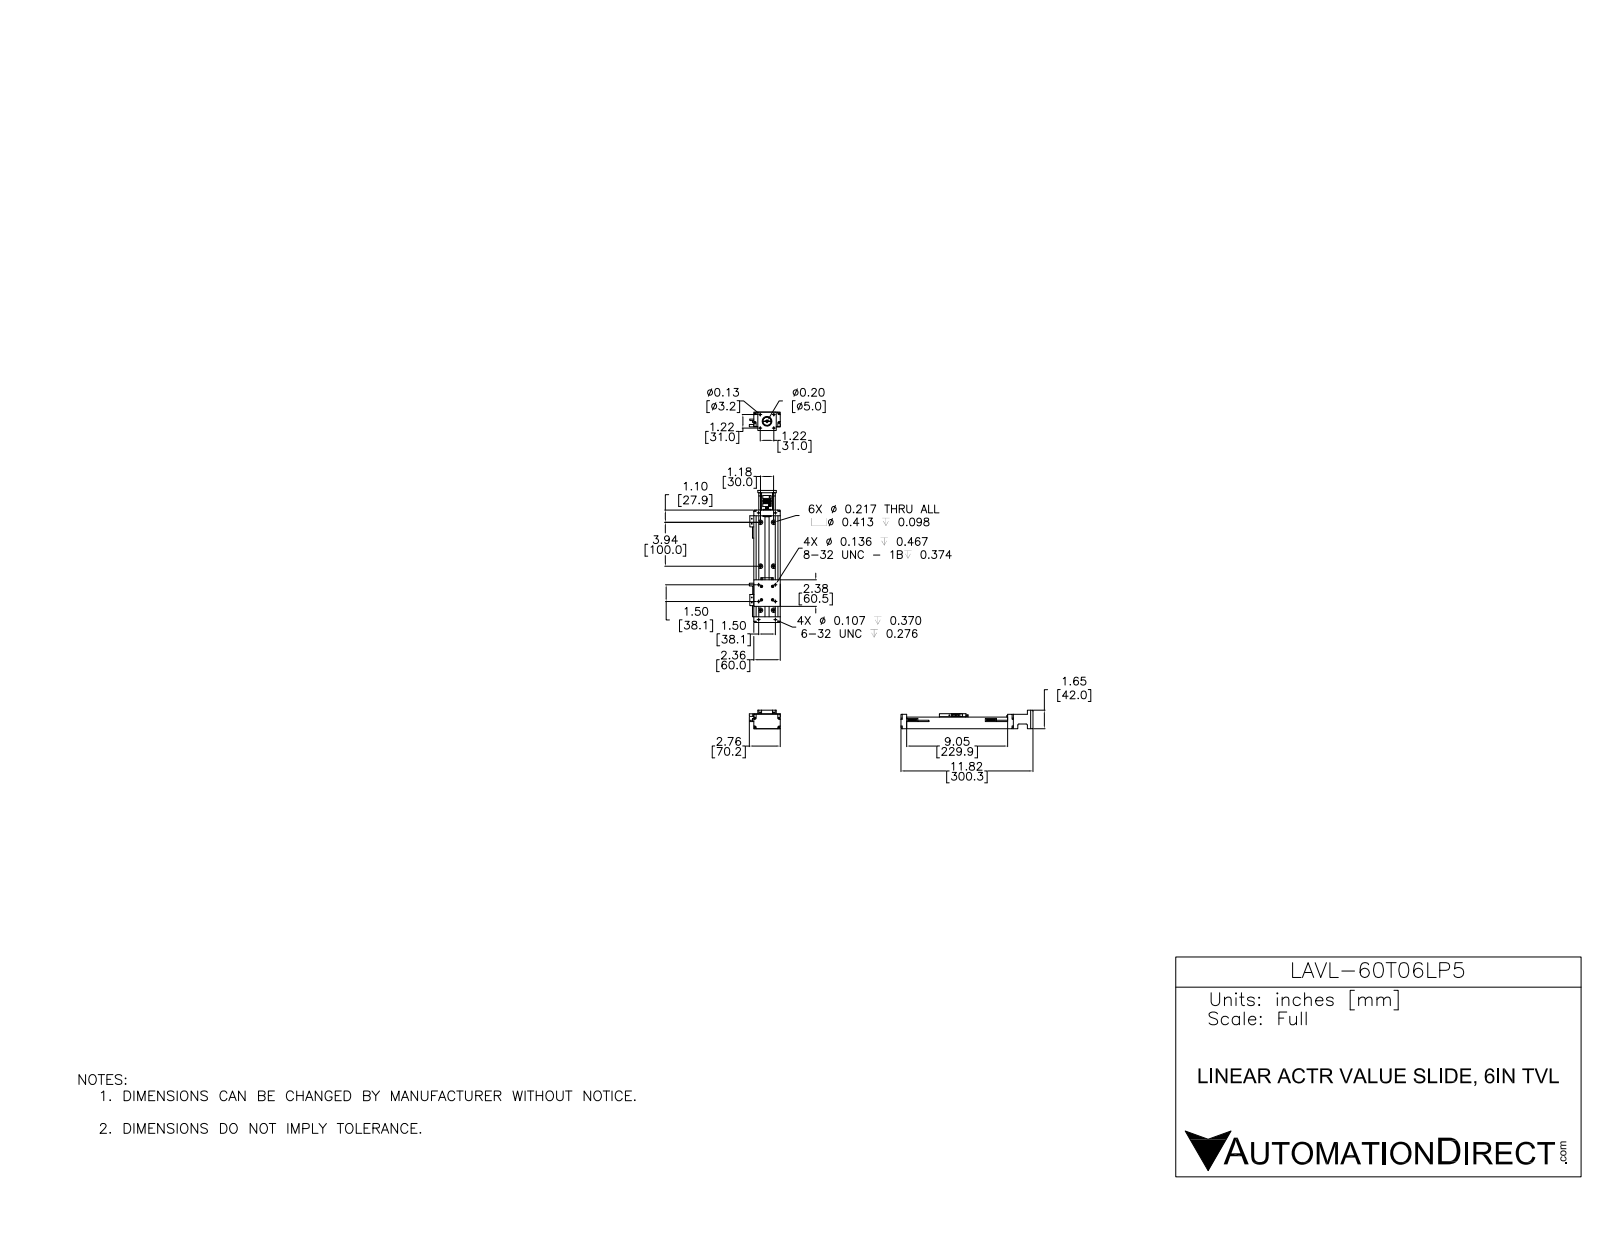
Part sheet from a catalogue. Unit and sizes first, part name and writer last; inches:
Units: inches
Overall size (bounding box): 11.824 × 2.762 × 1.654
Round holes (diameter × count): ⌀0.129 ×12, ⌀0.107 ×10, ⌀0.089 ×6, ⌀0.136 ×6, ⌀0.217 ×6, ⌀0.413 ×6, ⌀0.086 ×4, ⌀0.12 ×4, ⌀0.125 ×4, ⌀0.125 ×4, ⌀0.15 ×4, ⌀0.219 ×4
Round bosses / shafts (diameter × count): ⌀0.22 ×4, ⌀0.209 ×4, ⌀0.157 ×2, ⌀0.748 ×1, ⌀0.69 ×1, ⌀0.673 ×1, ⌀0.625 ×1, ⌀0.508 ×1
Partial cylindrical surfaces — rounded edges, fillets, slot ends (radius × count): R0.109 ×8, R0.047 ×4, R0.211 ×4, R0.266 ×4, R0.047 ×3, R0.188 ×3, R0.057 ×2, R0.062 ×2
Main face-to-face distances: 0.2, 2.162, 2.362, 1.962, 0.512, 9.562, 1.343, 1.143, 0.256, 0.25
Hole centre spacings: 1.089, 2.162, 1.22, 1.289, 1.5, 2.316, 0.292, 0.474
Volume: 17.92 in³ · Surface area: 216.4 in²
Bodies: 19 solids, 877 faces (330 planar, 376 cylindrical, 171 other)
Part name (STEP PRODUCT): LAVL-60T06LP5; LAVL-60T06LP5-CAR; LAVL-60T06LP5-RAIL
STEP written by: SolidWorks 2015 (AUTOMOTIVE_DESIGN)
